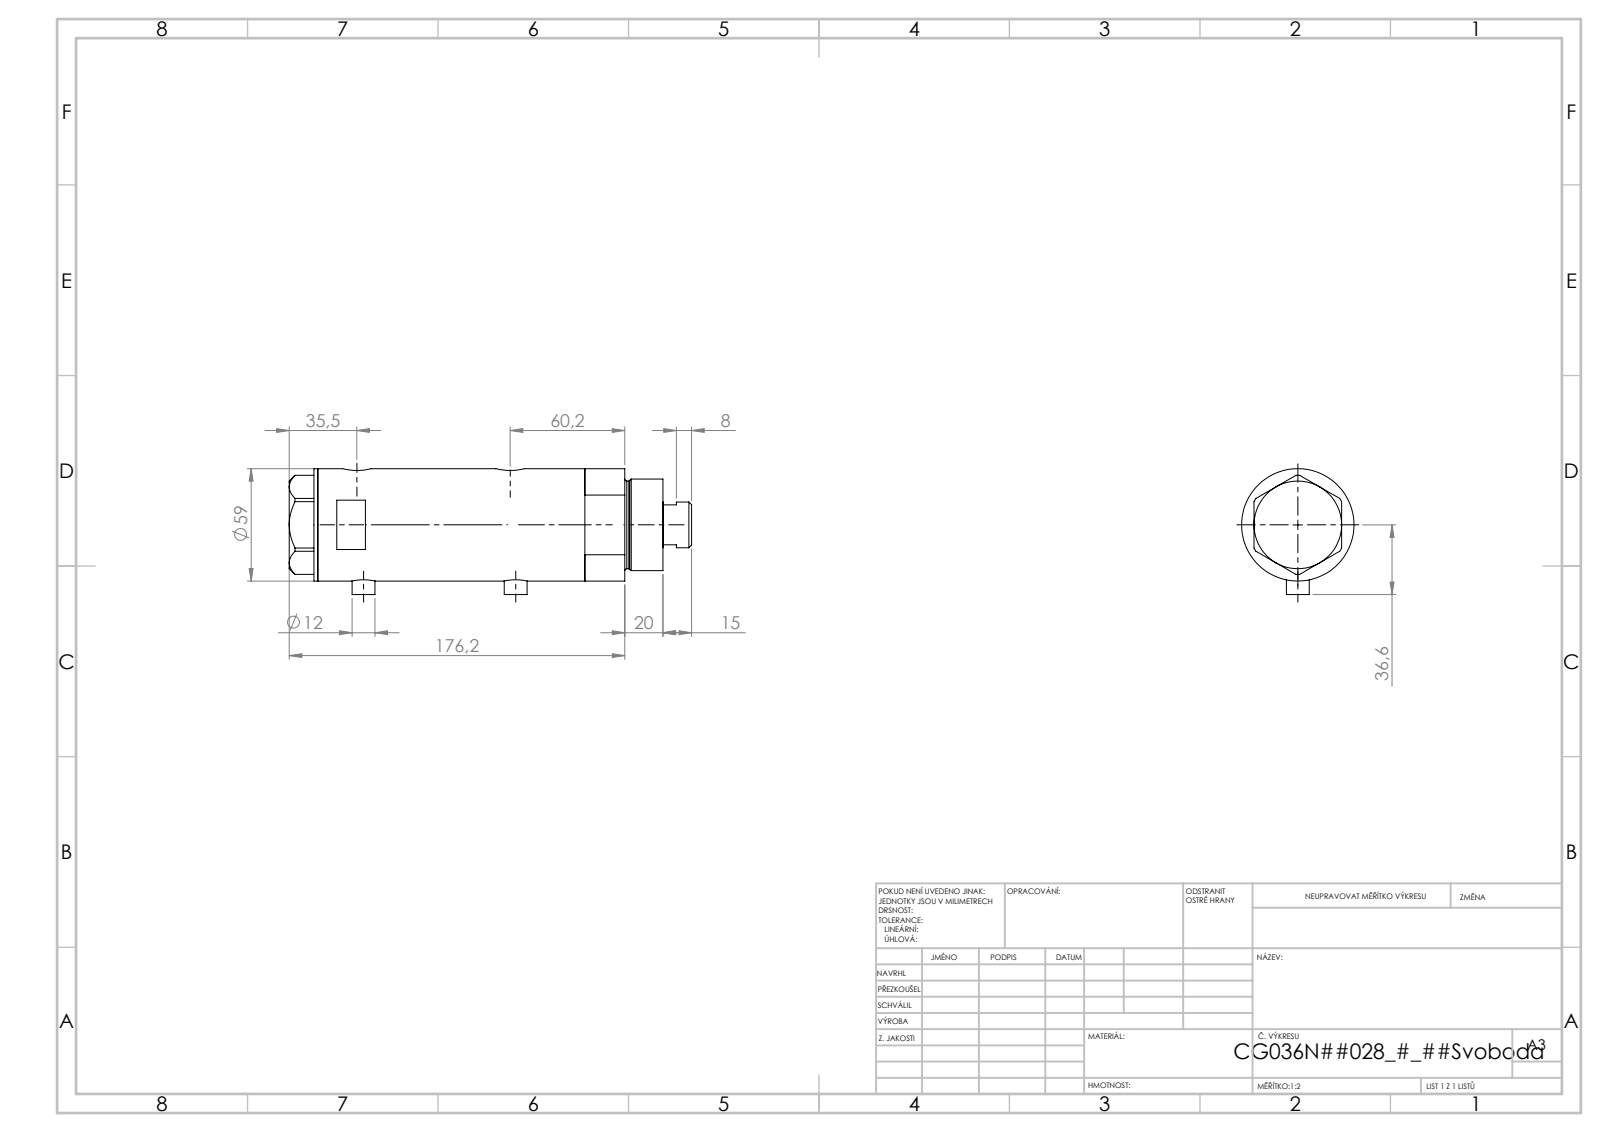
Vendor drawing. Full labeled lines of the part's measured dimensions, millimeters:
Part name (STEP PRODUCT): V270CG_MIDDLE; V270CG_FRONT; V270CG_BACK; V270CG_VC
STEP written by: SolidWorks 2019 (CONFIG_CONTROL_DESIGN)
Units: millimetres
Bodies: 4 solids, 126 faces (53 planar, 53 cylindrical, 20 other)
Overall size (bounding box): 211.25 × 66.1 × 59
Volume: 489 512 mm³ · Surface area: 101 103 mm²
Round holes (diameter × count): ⌀5 ×2, ⌀9.73 ×2, ⌀12.5 ×2, ⌀15 ×2, ⌀8.5 ×1, ⌀25 ×1, ⌀26.5 ×1, ⌀36 ×1, ⌀40 ×1, ⌀52 ×1
Round bosses / shafts (diameter × count): ⌀12 ×2, ⌀59 ×1, ⌀48 ×1, ⌀46 ×1, ⌀24 ×1
Main face-to-face distances: 102.2, 23.5, 78.7, 15, 38.5, 117.2, 2, 181.2, 196.2, 157.7
Hole centre spacings: 2.9, 3.5, 77, 79.9, 80.5, 83.4
